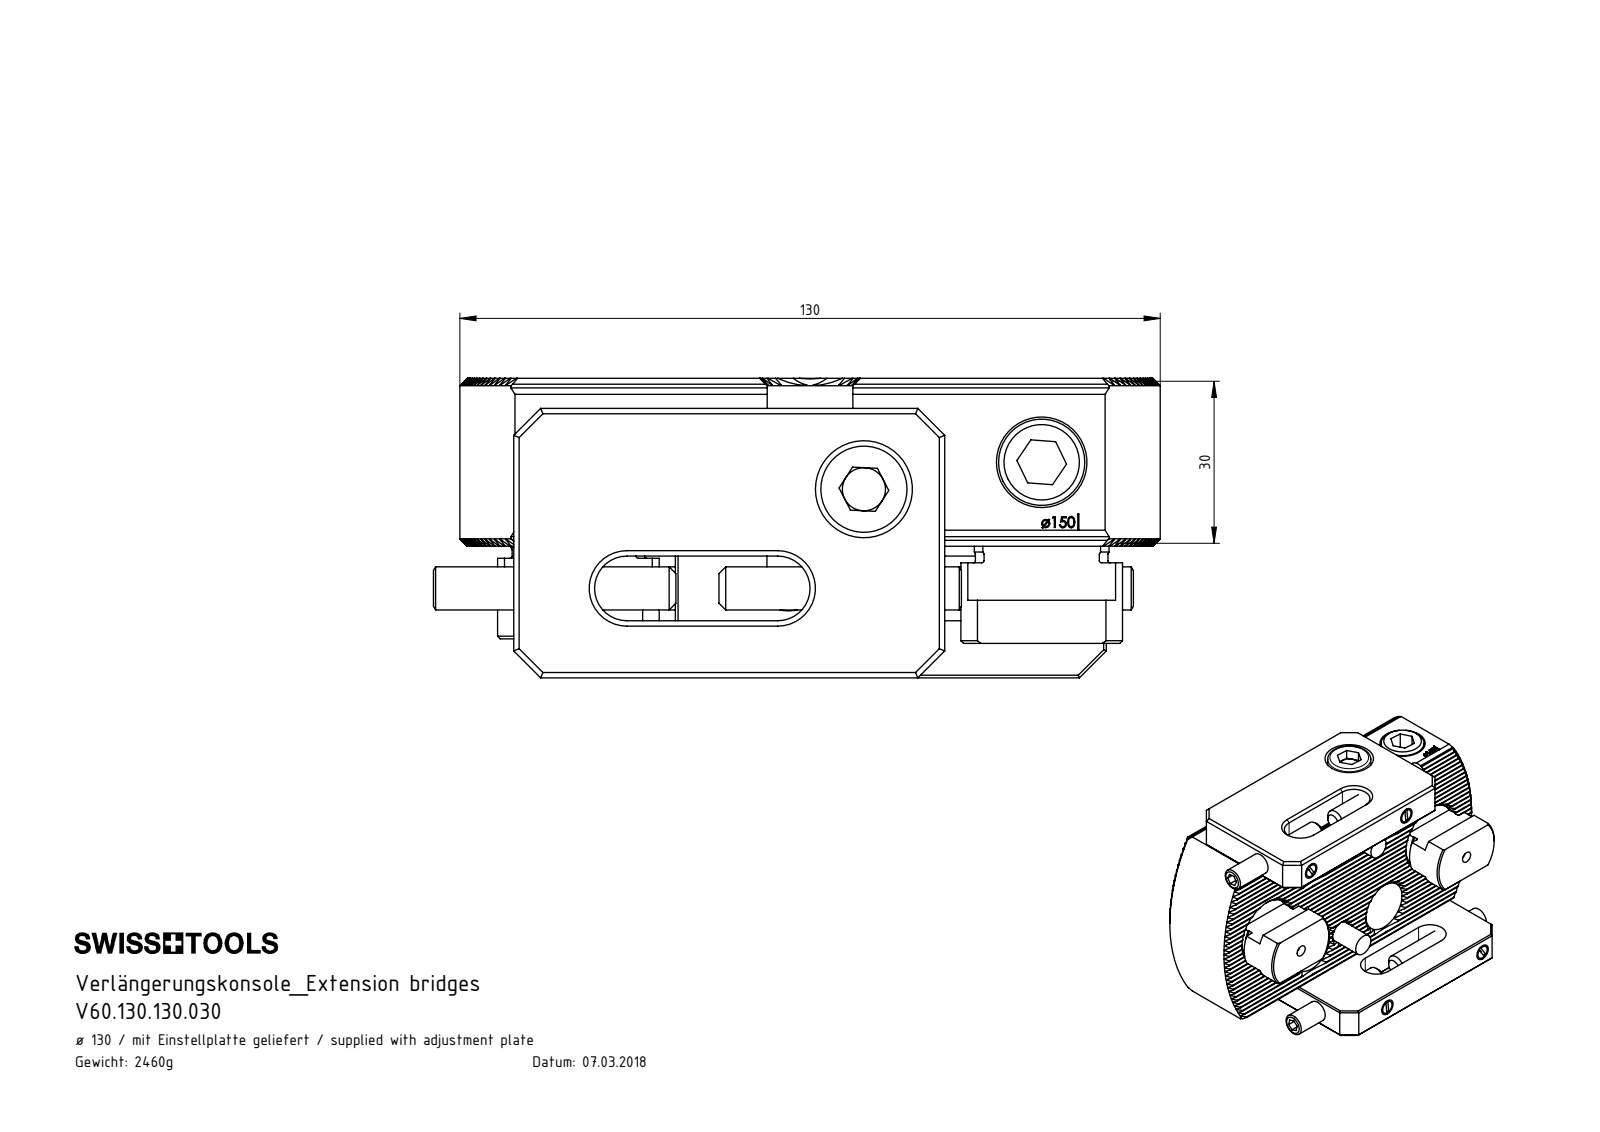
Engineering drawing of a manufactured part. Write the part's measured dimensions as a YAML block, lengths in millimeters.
part_name: "DIN 6912 - M10 x 12; VK1-ER1.001.030_A; ISO 8734 - 8 x 20 m6; VK1-ER2.201.010_A_vorgespannt (+8 more)"
step_written_by: "SolidWorks 2017 (AUTOMOTIVE_DESIGN)"
units: millimeters
bodies: {solids: 27, faces: 1459, planar: 964, cylindrical: 294, other: 201}
overall_size: [139.81, 95, 55.58]
volume: 319015
surface_area: 100766
round_holes:
  - {diameter: 5, count: 4}
  - {diameter: 6, count: 4}
  - {diameter: 6.8, count: 4}
  - {diameter: 13, count: 4}
  - {diameter: 19, count: 4}
  - {diameter: 2, count: 2}
  - {diameter: 8, count: 2}
  - {diameter: 8.5, count: 2}
  - {diameter: 10.5, count: 2}
  - {diameter: 11, count: 2}
  - {diameter: 14, count: 2}
  - {diameter: 18, count: 2}
round_bosses_or_shafts:
  - {diameter: 16, count: 4}
  - {diameter: 6, count: 4}
  - {diameter: 10, count: 2}
  - {diameter: 8, count: 2}
partial_cylinders:
  - {radius: 0.14, count: 66}
  - {radius: 2, count: 8}
  - {radius: 6, count: 4}
  - {radius: 12.3, count: 2}
  - {radius: 15, count: 2}
  - {radius: 7.95, count: 1}
  - {radius: 65, count: 1}
face_to_face_distances: [12, 82, 70, 0.5, 82.5, 11.5, 1.73, 70.5, 94, 71]
hole_center_spacings: [31.24, 65.15, 86, 2.05, 6.67, 7.9, 15, 17]
